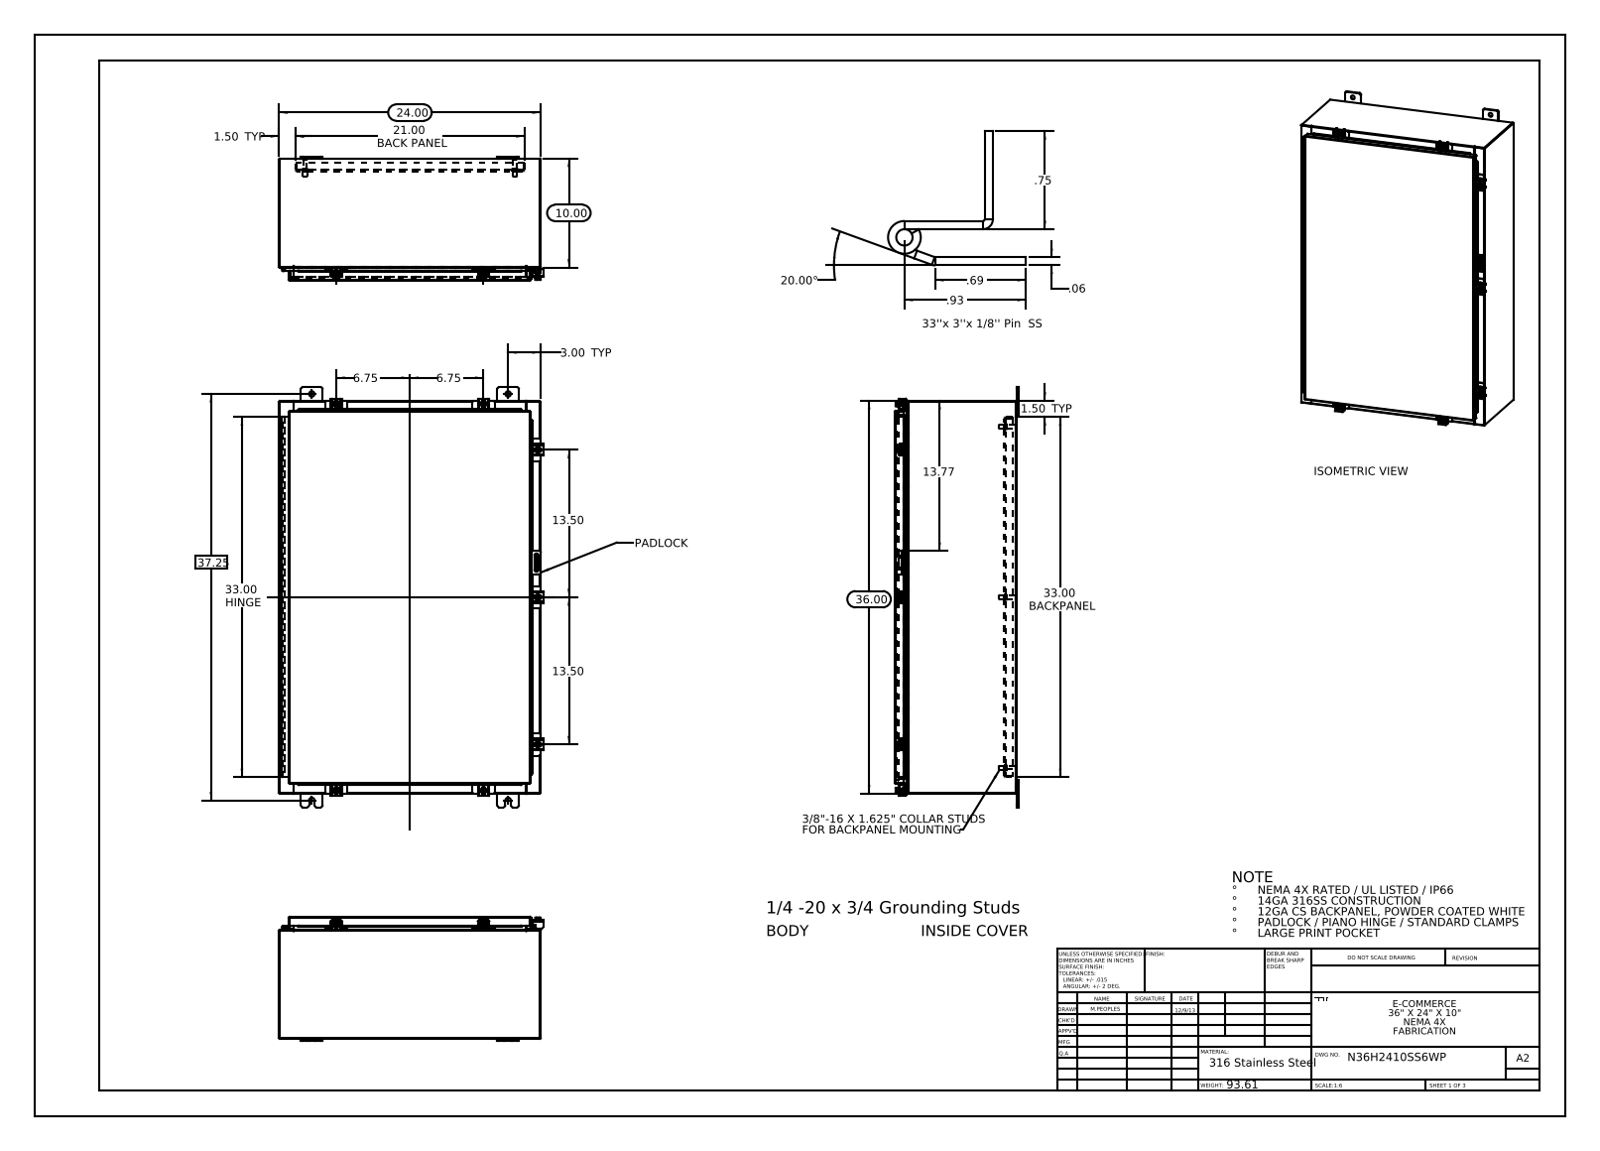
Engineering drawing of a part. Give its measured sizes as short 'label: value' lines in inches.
name: N36H2410SS6WP 22101002; N36H2410SS6WP 125 Pin Hinge; N36H2410SS6WP Padlock Hasp; N36H2410SS6WP Backpanel (+8 more)
written by: SolidWorks 2013 (CONFIG_CONTROL_DESIGN)
unit: in
bodies: 54 solids, 2184 faces (1138 planar, 922 cylindrical, 124 other)
size: 38.5 × 24.211 × 11.389
volume: 328.4 in³; area: 8 226 in²
holes: 10× ⌀0.5, 7× ⌀0.213, 7× ⌀0.26, 2× ⌀0.125, 1× ⌀0.125
bosses: 8× ⌀0.25, 7× ⌀0.5, 7× ⌀0.399, 6× ⌀0.625, 6× ⌀0.375, 6× ⌀0.33
rounds: 34× R0.06, 27× R0.013, 24× R0.19, 21× R0.088, 14× R0.12, 14× R0.141, 11× R0.05, 10× R0.08
face distances: 0.075, 11.126, 11.201, 11.051, 0.104, 23.925, 1, 1.075, 10.051, 10.126
hole spacings: 13.5, 15.625, 17.957, 24.793, 33.474, 37.154, 19.25, 1.858
